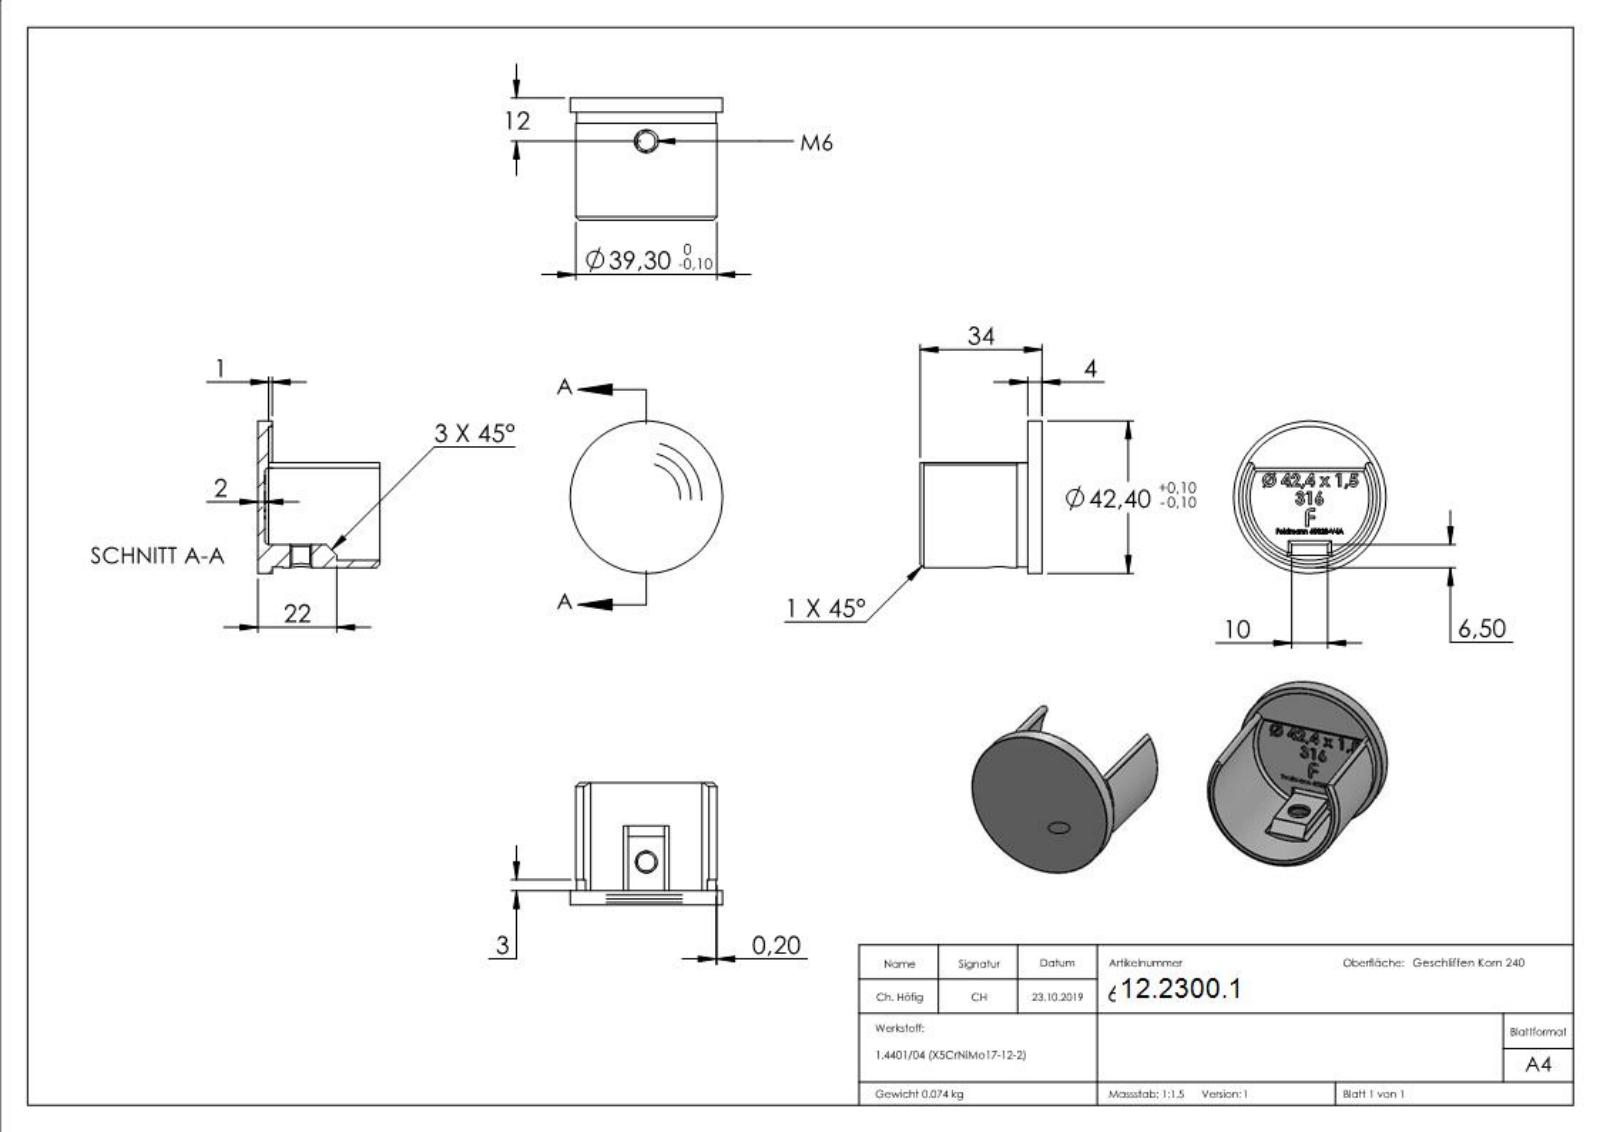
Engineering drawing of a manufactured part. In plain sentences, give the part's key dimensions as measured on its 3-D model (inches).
The part is named "60328-V4A". Its 3-D file was written by "SolidWorks 2015 (CONFIG_CONTROL_DESIGN)". It is 1 solid with 429 faces: 256 planar, 14 cylindrical and 159 other. Overall it measures 1.669 by 1.669 by 1.339 inches. Its volume is 0.569 cubic inches and its surface area 13.12 square inches. Round holes: 1 of diameter 0.197, 1 of diameter 1.547. Round bosses or shafts: 1 of diameter 1.669. Partial cylindrical surfaces (rounded edges, fillets, slot ends): 6 of radius 0.039, 2 of radius 0.04, 1 of radius 0.693, 1 of radius 0.766. The main face-to-face distances are 0.079, 0.039, 0.118, 0.157, 1.181, 1.22, 1.26, 1.339, 0.075, 0.083.
